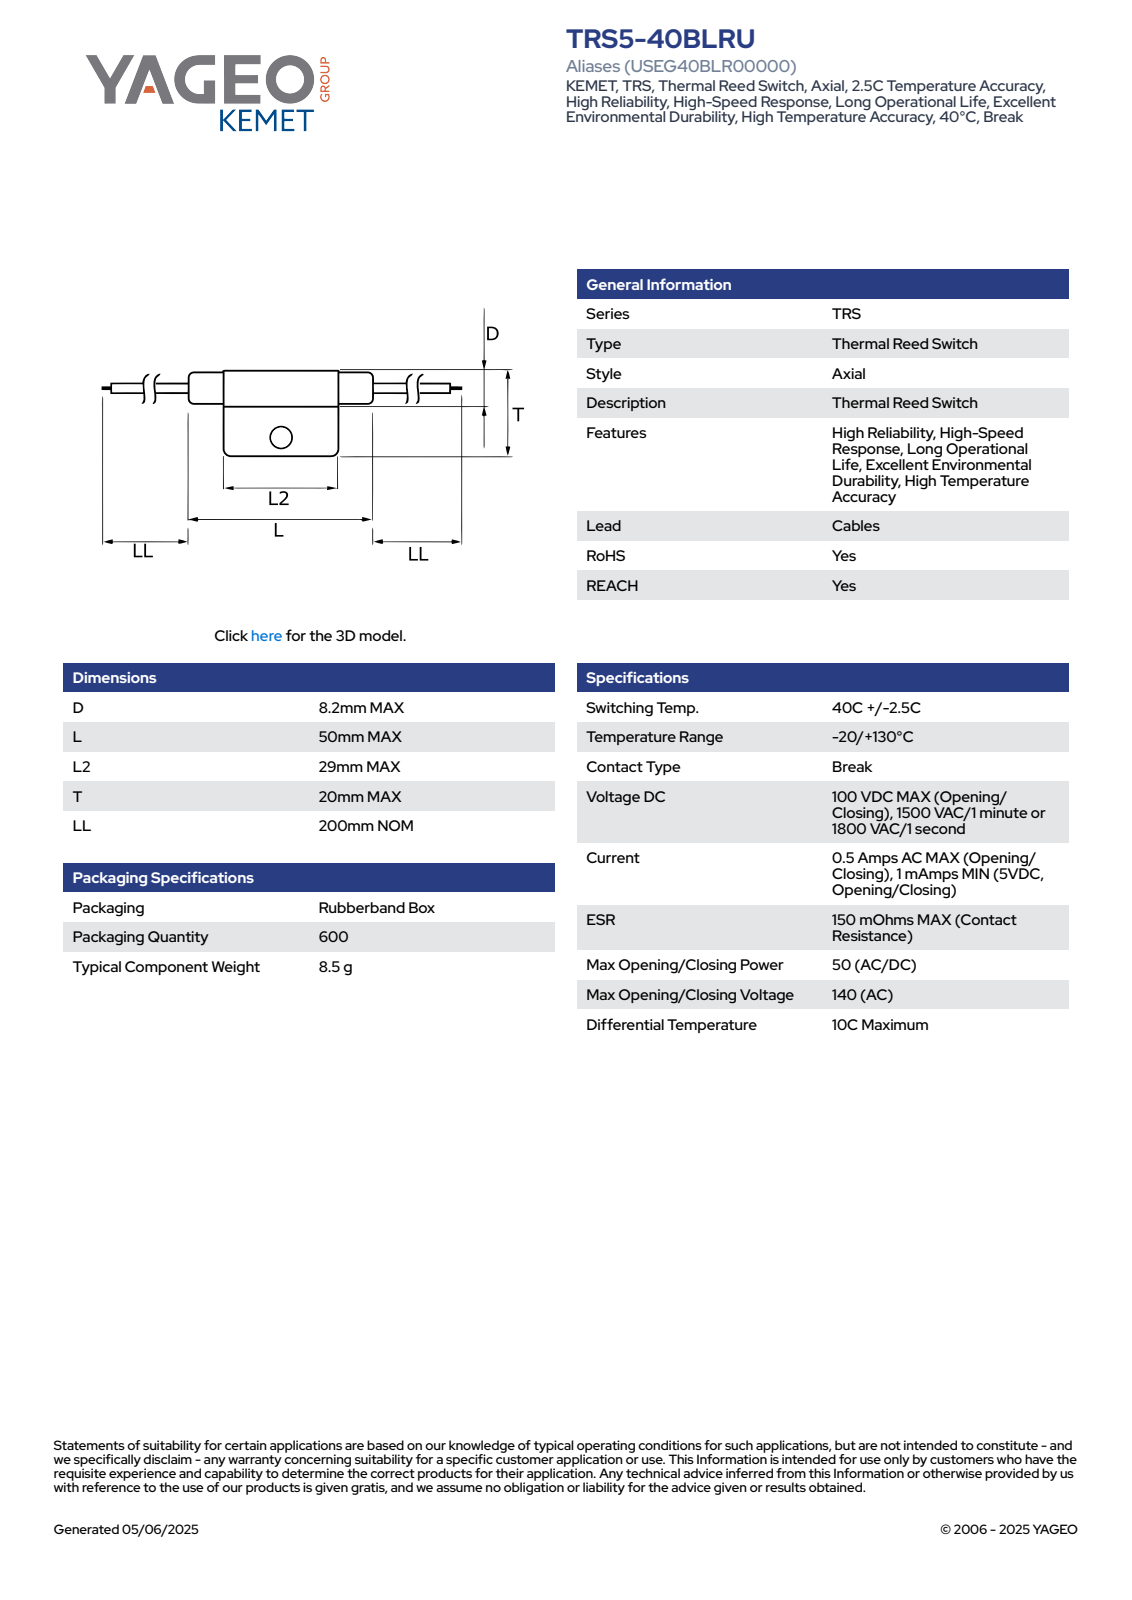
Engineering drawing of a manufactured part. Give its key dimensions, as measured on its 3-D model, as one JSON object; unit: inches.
{"part_name": "Default", "step_written_by": "SolidWorks 2014 (AUTOMOTIVE_DESIGN)", "units": "inches", "bodies": {"solids": 1, "faces": 90, "planar": 33, "cylindrical": 22, "other": 35}, "overall_size": [17.717, 0.787, 0.323], "volume_in3": 0.188, "surface_area_in2": 5.273, "round_holes": [[0.132, 1]], "round_bosses_or_shafts": [[0.323, 1], [0.315, 1], [0.039, 1], [0.02, 1]], "partial_cylinders_radius": [[0.079, 2], [0.161, 1]], "face_to_face_distances": [0.02, 1.969, 0.413, 1.555, 1.142, 7.48, 7.894, 9.035, 9.449, 16.929]}
